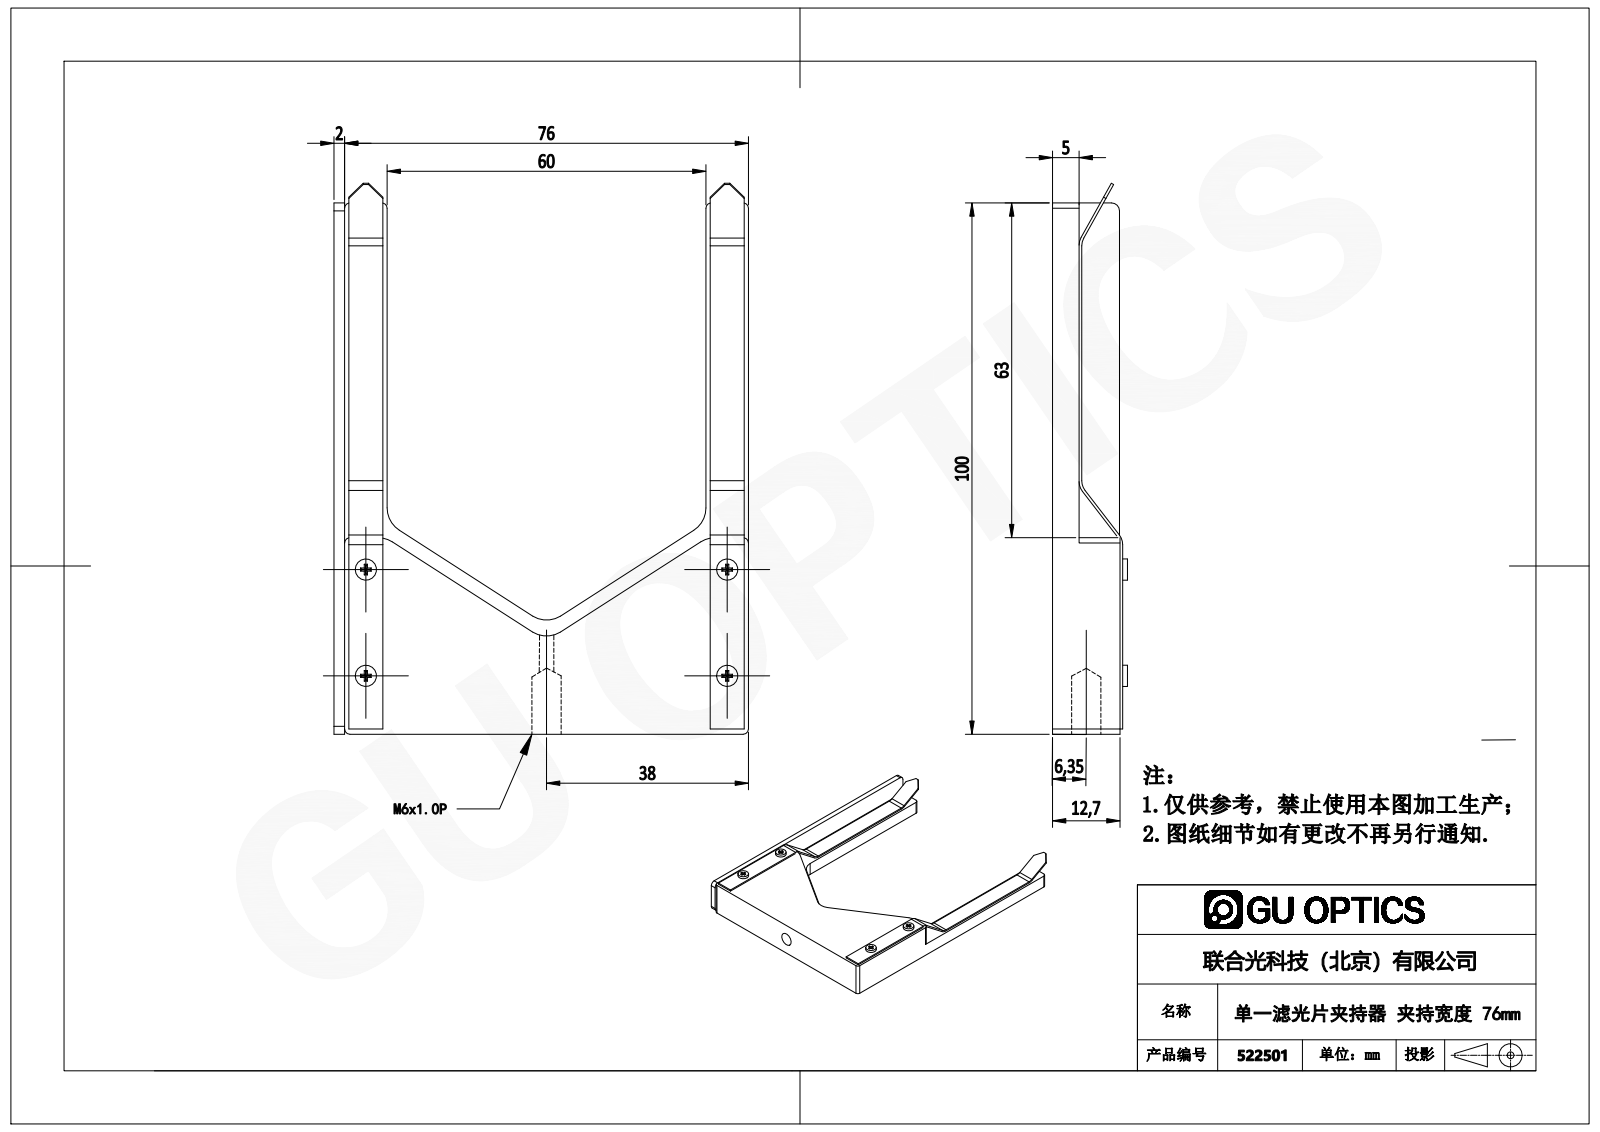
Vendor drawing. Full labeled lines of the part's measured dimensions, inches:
Part name (STEP PRODUCT): SFH-3
STEP written by: SolidWorks 2012 (CONFIG_CONTROL_DESIGN)
Units: inches
Bodies: 0 solids, 160 faces (124 planar, 34 cylindrical, 2 other)
Overall size (bounding box): 4.083 × 3.071 × 0.555
Round holes (diameter × count): ⌀0.102 ×1, ⌀0.197 ×1
Round bosses / shafts (diameter × count): ⌀0.157 ×4, ⌀0.118 ×2
Partial cylindrical surfaces — rounded edges, fillets, slot ends (radius × count): R0.039 ×8, R0.197 ×6, R0.059 ×4, R0.118 ×4
Main face-to-face distances: 0.5, 0.303, 0.02, 0.197, 0.079, 0.283, 3.071, 2.992, 2.677, 0.217
